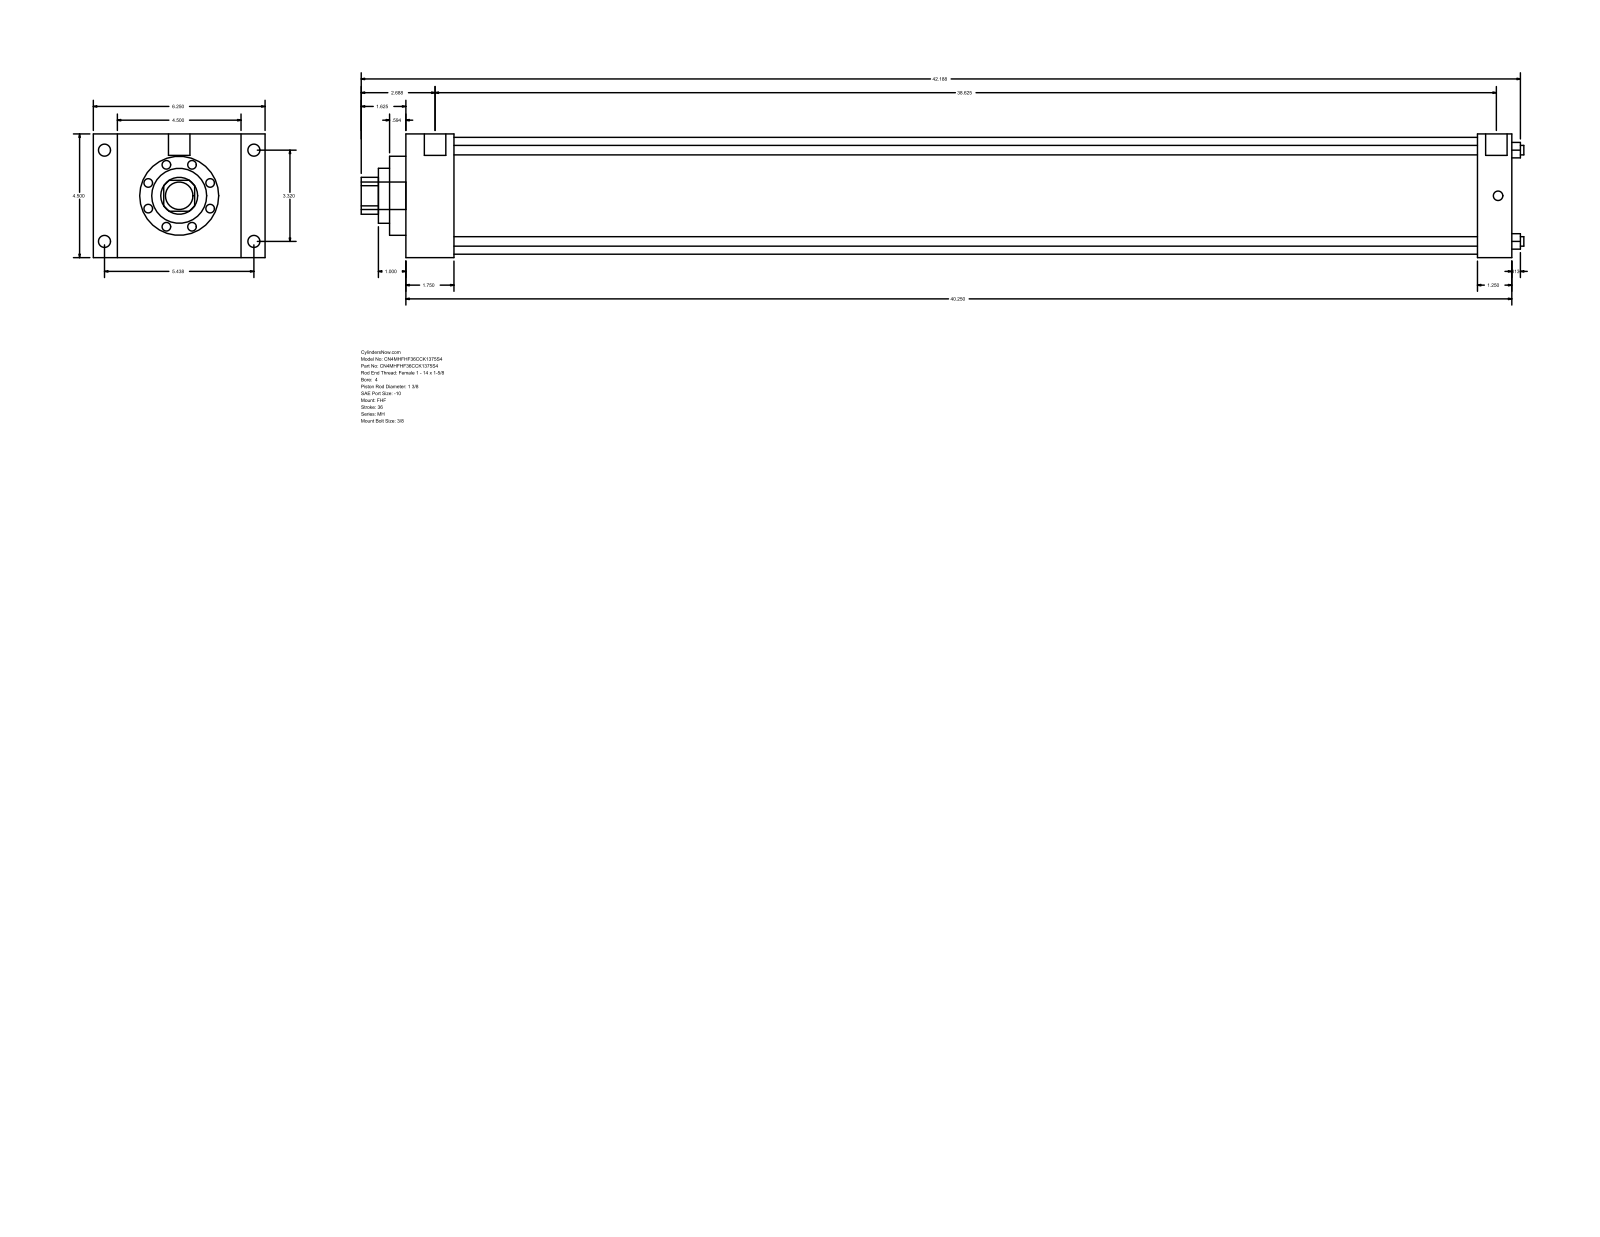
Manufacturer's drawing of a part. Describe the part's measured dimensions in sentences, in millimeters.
The part is named "MH_FHF__0400_1.375". Its 3-D file was written by "GSSL Pune (CONFIG_CONTROL_DESIGN)". It is 0 solids with 90 faces: 61 planar, 29 cylindrical and 0 other. Overall it measures 1074.74 by 158.75 by 114.3 millimeters. Round holes: 4 of diameter 8.76, 1 of diameter 34.92, 1 of diameter 50.8, 1 of diameter 73.03, 1 of diameter 107.95. Round bosses or shafts: 4 of diameter 11.13, 4 of diameter 8.73, 2 of diameter 19.84, 1 of diameter 25.4. Partial cylindrical surfaces (rounded edges, fillets, slot ends): 1 of radius 17.06. The main face-to-face distances are 114.3, 1022.35, 44.45, 977.9, 22.23, 136.53, 158.76, 990.61, 946.16, 31.74. The hole center spacings are 59.62, 84.32, 119.25.
